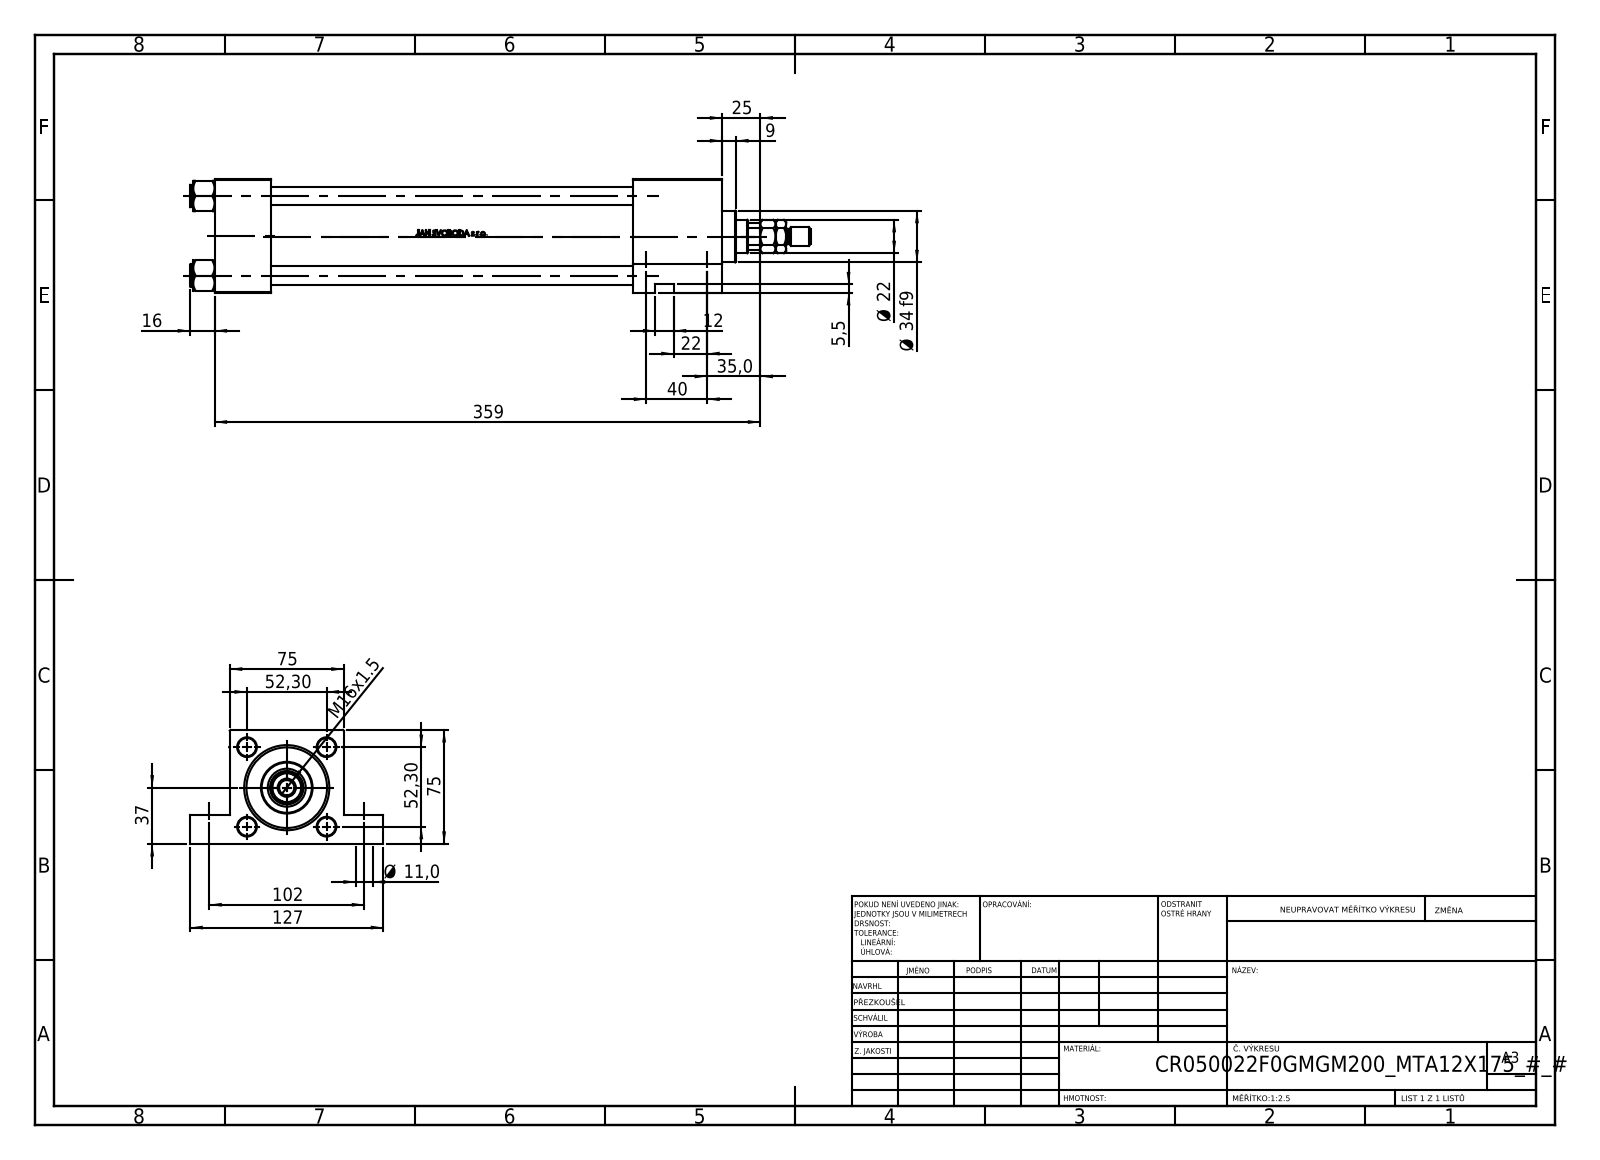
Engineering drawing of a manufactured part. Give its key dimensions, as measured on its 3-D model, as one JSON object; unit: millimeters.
{"part_name": "V215CR_VCP_F; NUT_M5_F; MTA; V215_VC_A (+2 more)", "step_written_by": "SolidWorks 2019 (CONFIG_CONTROL_DESIGN)", "units": "millimeters", "bodies": {"solids": 12, "faces": 1152, "planar": 452, "cylindrical": 130, "other": 570}, "overall_size": [408, 127, 75], "volume_mm3": 953443, "surface_area_mm2": 258194, "round_holes": [[11, 4], [12, 4], [7, 2], [30, 2], [10.5, 1], [17, 1], [20.96, 1], [22, 1], [25, 1], [41, 1], [50, 1], [53, 1]], "round_bosses_or_shafts": [[15, 4], [56, 1], [34, 1], [12, 1], [10, 1]], "partial_cylinders_radius": [[10.5, 1]], "face_to_face_distances": [75, 37, 297, 334, 275, 238, 59, 19, 305.3, 268.3], "hole_center_spacings": [52.3, 36.63, 37.34, 40, 73.96, 102, 109.56, 273.5]}
